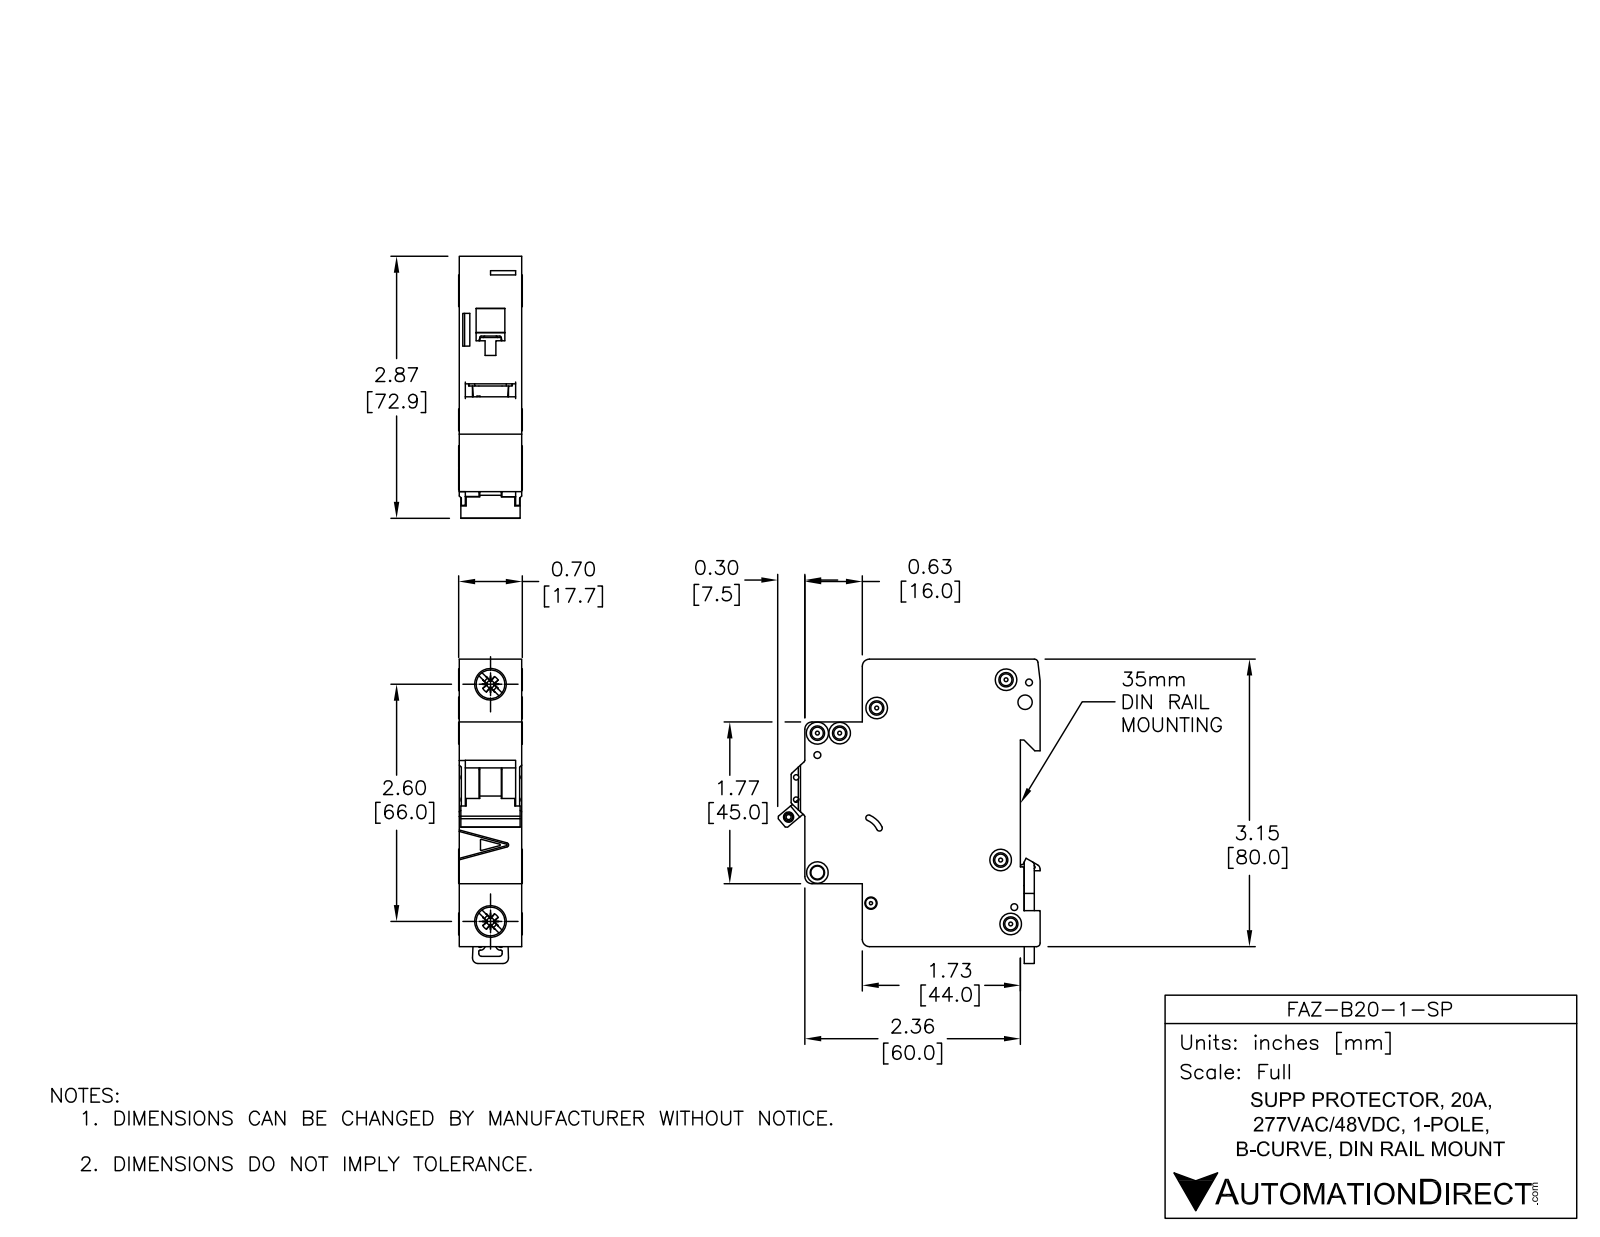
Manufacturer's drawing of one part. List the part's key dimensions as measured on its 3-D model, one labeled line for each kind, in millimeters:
Part name (STEP PRODUCT): FAZ-B20-1-SP
STEP written by: SolidWorks 2014 (AUTOMOTIVE_DESIGN)
Units: millimetres
Bodies: 5 solids, 558 faces (235 planar, 202 cylindrical, 121 other)
Overall size (bounding box): 84.78 × 73.04 × 17.7
Volume: 74 935 mm³ · Surface area: 19 545 mm²
Round holes (diameter × count): ⌀3.6 ×6, ⌀1.9 ×3, ⌀1.09 ×2, ⌀1.5 ×2, ⌀4 ×2, ⌀7.15 ×2, ⌀2.15 ×1, ⌀2.2 ×1, ⌀2.55 ×1, ⌀3.3 ×1, ⌀3.4 ×1
Round bosses / shafts (diameter × count): ⌀6 ×4, ⌀8.2 ×2, ⌀2.5 ×1
Partial cylindrical surfaces — rounded edges, fillets, slot ends (radius × count): R0.25 ×30, R0.5 ×13, R2 ×8, R0.2 ×5, R1 ×4, R0.8 ×2, R3 ×2, R1.5 ×1
Main face-to-face distances: 17.5, 79.48, 5.5, 49.5, 44, 65.5, 60, 16, 1.75, 15.75
Hole centre spacings: 6.2, 13.64, 4.81, 5.19, 5.61, 6.1, 6.44, 8.19
